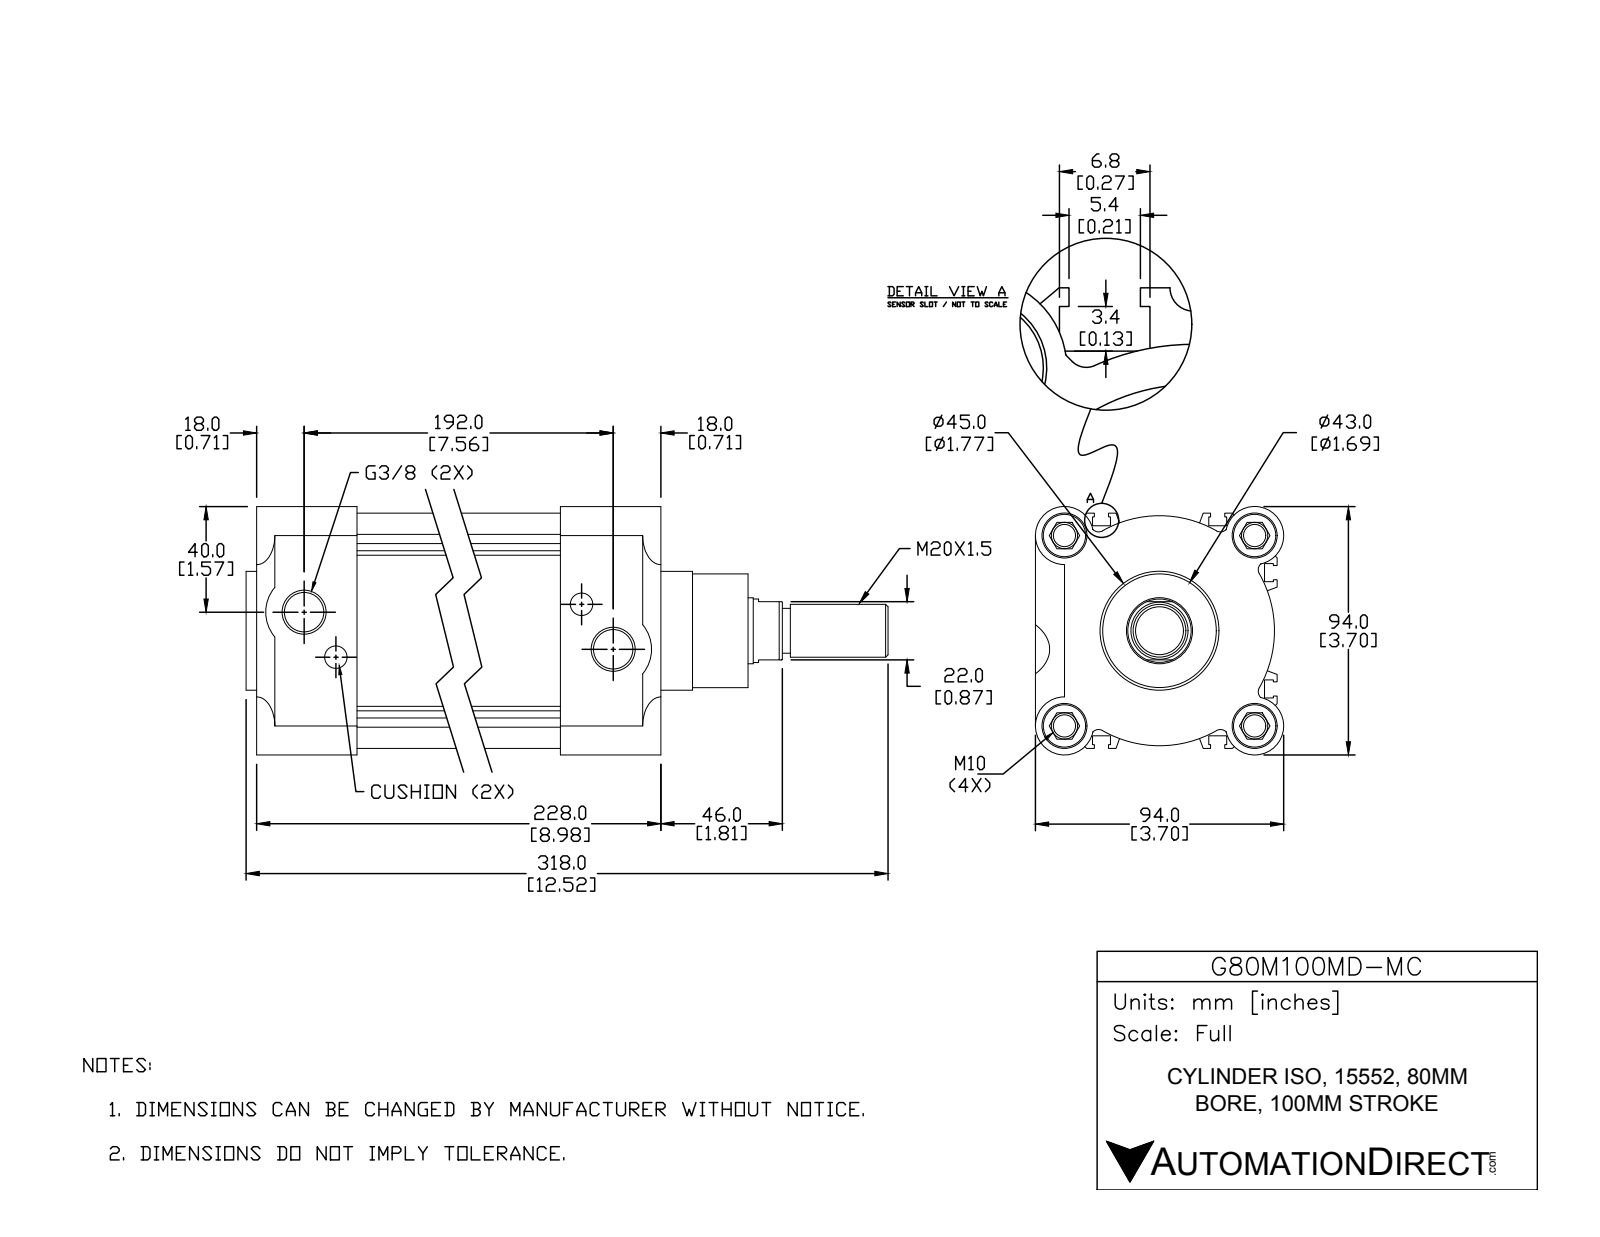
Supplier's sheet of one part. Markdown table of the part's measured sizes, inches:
| quantity | value |
| --- | --- |
| part name | G80M100MD-MC; 80121-HR; 80-100-110.5-B; 80121100-R (+1 more) |
| STEP written by | SolidWorks 2015 (CONFIG_CONTROL_DESIGN) |
| units | inches |
| bodies | 4 solids, 418 faces (236 planar, 138 cylindrical, 44 other) |
| overall size | 12.52 × 3.701 × 3.701 |
| volume | 78.98 in³ |
| surface area | 390.4 in² |
| round holes (diameter × count) | 0.33 × 4, 0.669 × 4, 0.335 × 2, 0.589 × 2, 0.984 × 1 |
| round bosses / shafts (diameter × count) | 0.63 × 4, 3.15 × 1, 1.772 × 1, 1.693 × 1, 0.945 × 1, 0.787 × 1, 0.669 × 1 |
| partial cylindrical surfaces (radius × count) | 0.004 × 6, 0.118 × 6, 0.315 × 4, 0.433 × 4, 0.571 × 2, 1.693 × 1, 1.713 × 1 |
| main face-to-face distances | 0.394, 5.591, 1.496, 7.48, 1.89, 7.087, 1.654, 0.187, 3.317, 5.984 |
| hole center spacings | 2.004, 2.835, 0.819, 4.009, 7.087, 6.661, 7.579 |
